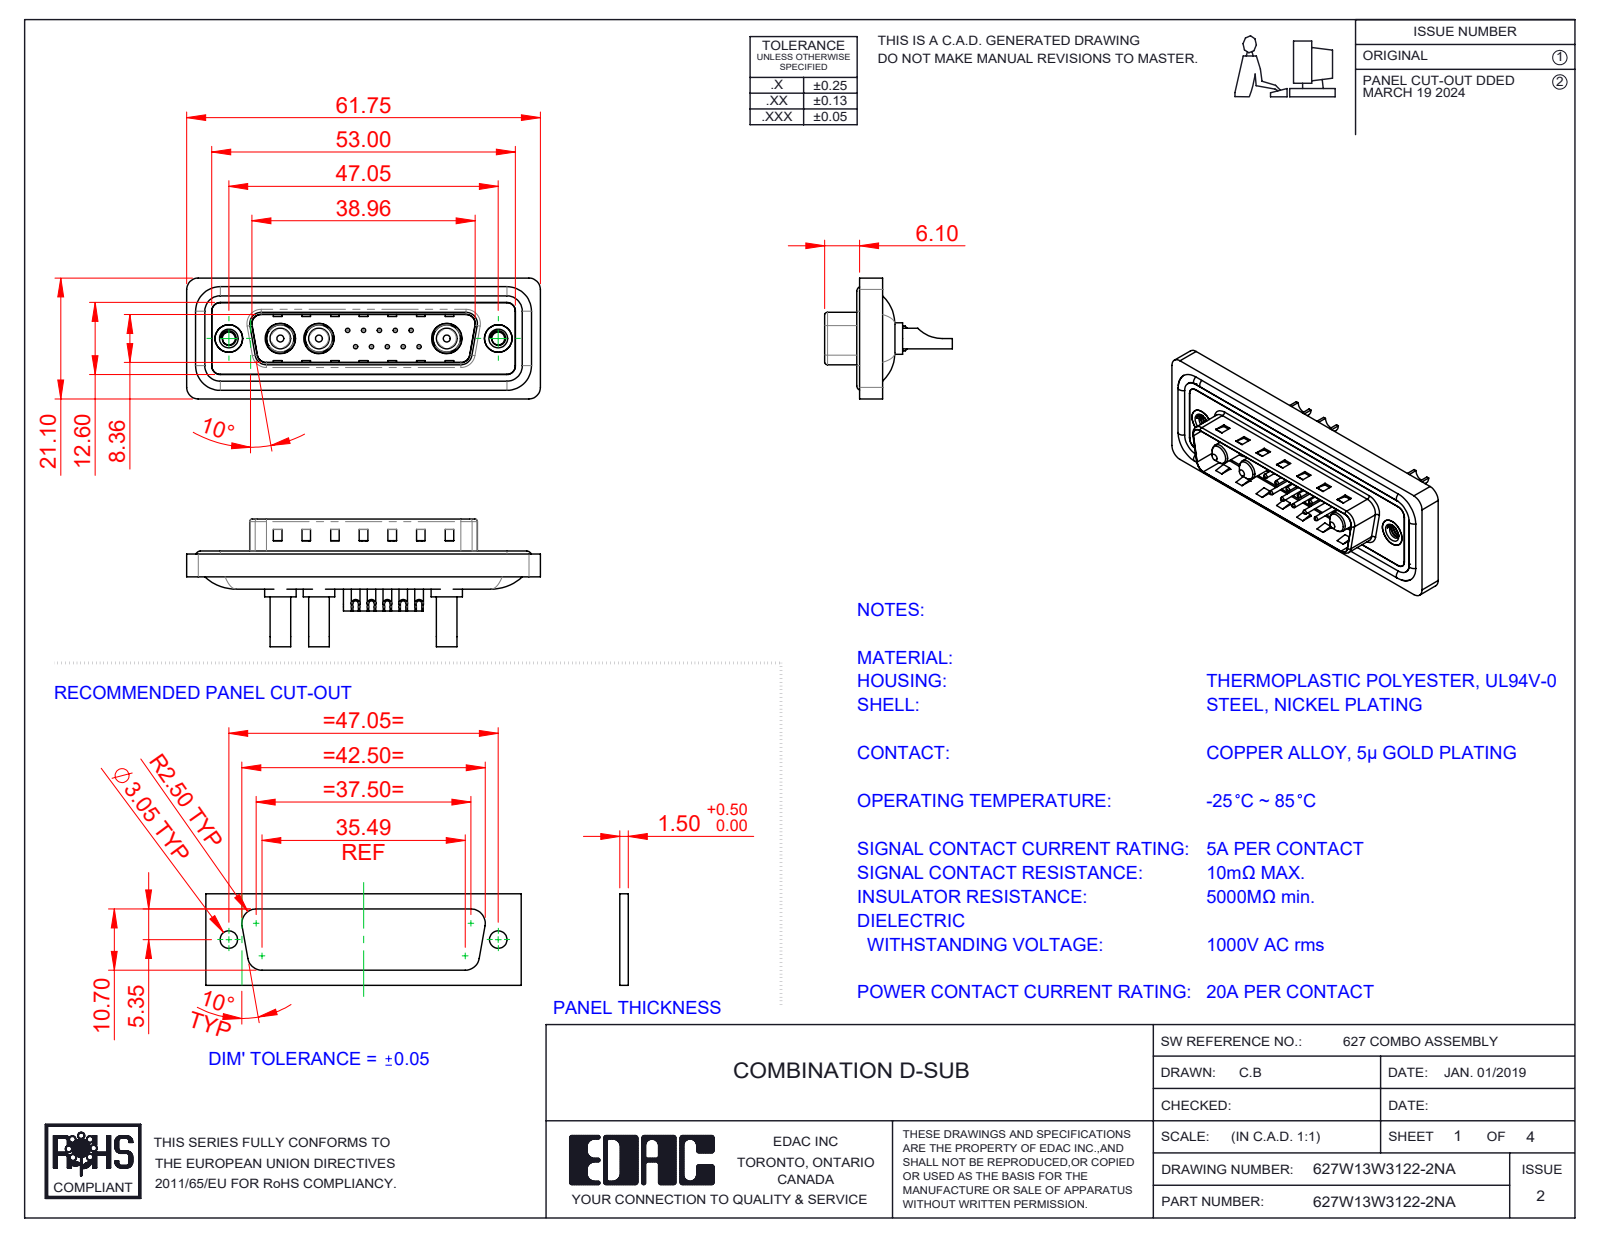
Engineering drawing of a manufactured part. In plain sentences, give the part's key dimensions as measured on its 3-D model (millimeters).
The part is named "627Combo Shell Rear_25 Contacts; Power Pin_20A SC; 627Combo Waterproof Housing_25 Contacts; 627Combo Shell Front_25 Contacts (+5 more)". Its 3-D file was written by "SolidWorks 2023 (CONFIG_CONTROL_DESIGN)". It is 23 solids with 986 faces: 338 planar, 416 cylindrical and 232 other. Overall it measures 61.75 by 22.3 by 21.1 millimeters. Its volume is 7 391 cubic millimeters and its surface area 12 199 square millimeters. Round holes: 10 of diameter 0.75, 10 of diameter 1, 10 of diameter 1.6, 10 of diameter 2, 3 of diameter 2.7, 3 of diameter 4.85, 3 of diameter 5.3, 2 of diameter 2.26, 2 of diameter 4, 2 of diameter 4.8, 2 of diameter 5. Round bosses or shafts: 10 of diameter 1.5, 4 of diameter 1.6, 3 of diameter 5.5, 3 of diameter 5.2, 3 of diameter 4.75, 3 of diameter 3.75, 3 of diameter 3.6, 2 of diameter 4.9. Partial cylindrical surfaces (rounded edges, fillets, slot ends): 22 of radius 1.5, 18 of radius 2, 8 of radius 0.5, 8 of radius 1.6, 6 of radius 1, 4 of radius 0.25, 4 of radius 0.6, 4 of radius 0.65. The main face-to-face distances are 0.4, 1.5, 1.1, 1.6, 0.5, 3.1, 2.9, 0.82, 9.58, 4.1. The hole center spacings are 3.16, 2.77, 5.04, 5.54, 7.49, 5.03, 8.31, 10.11.
